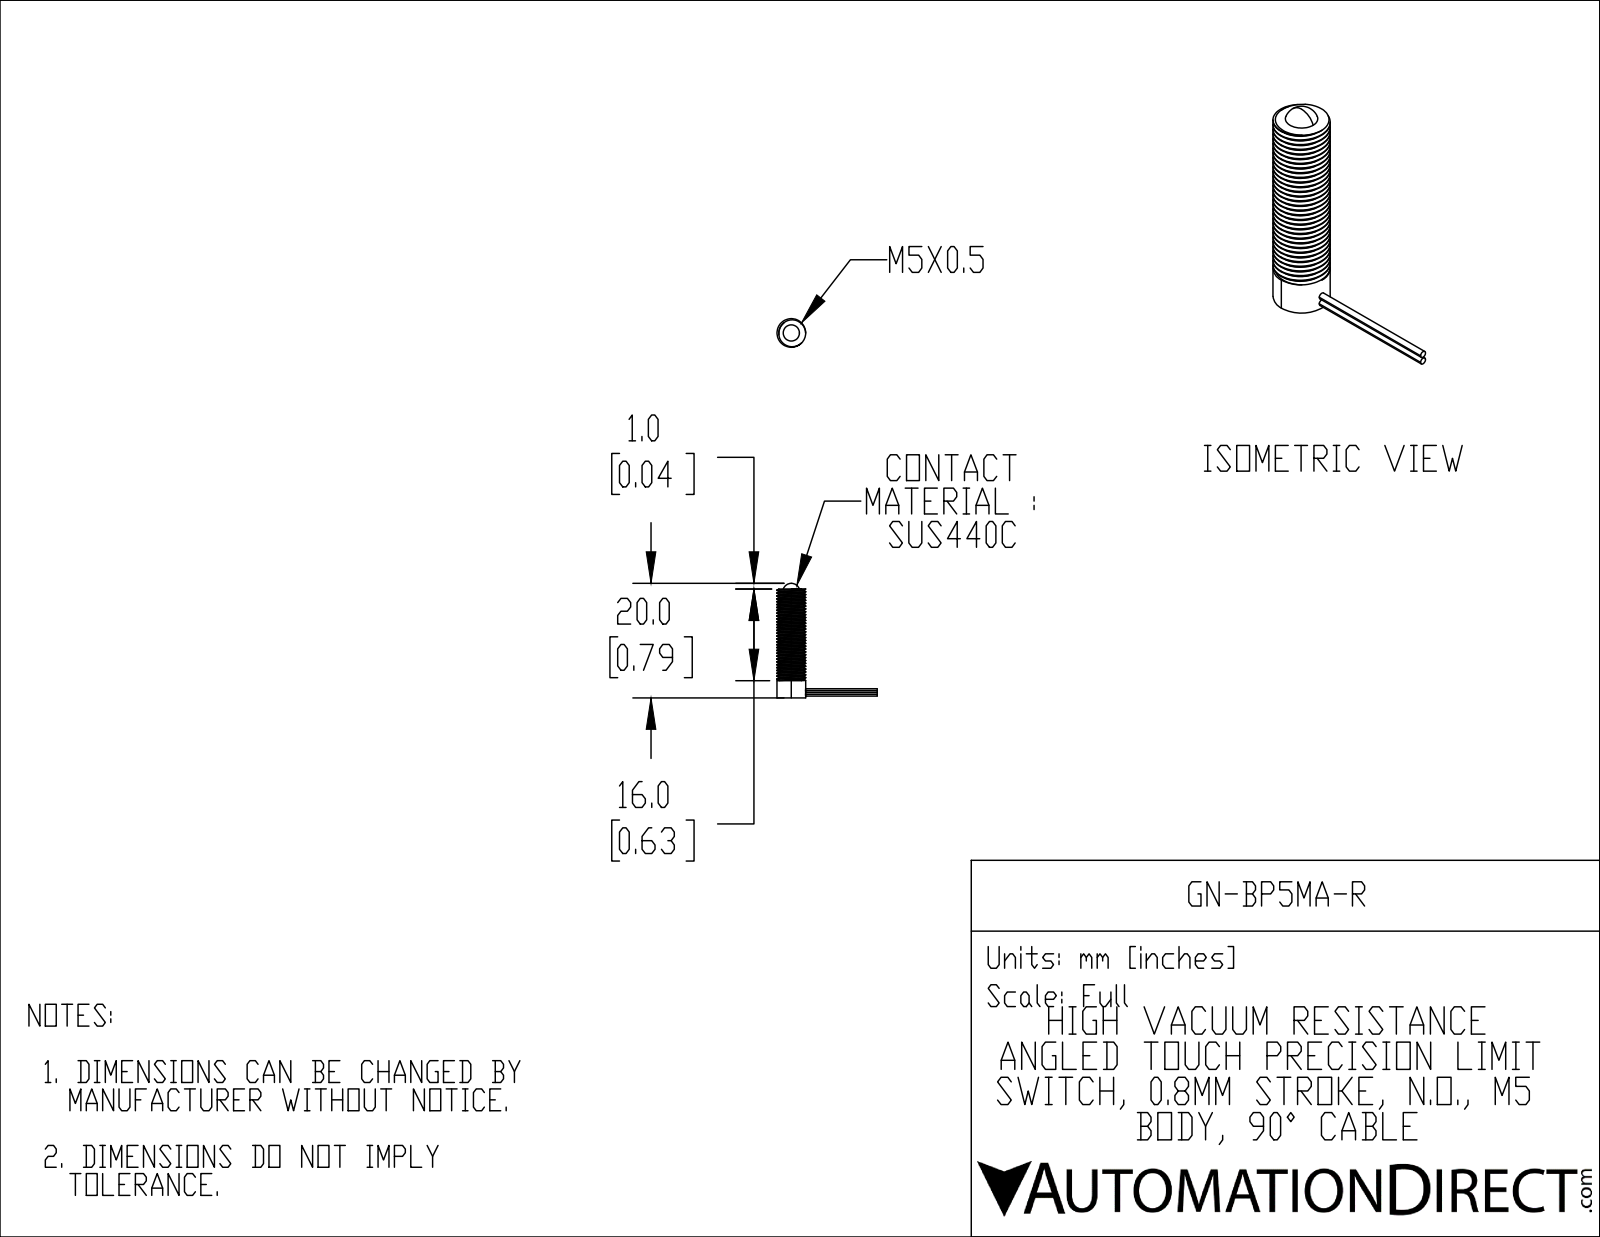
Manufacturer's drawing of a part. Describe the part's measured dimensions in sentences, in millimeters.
The part is named "GN-BP5MA-R". Its 3-D file was written by "SolidWorks 2020 (CONFIG_CONTROL_DESIGN)". It is 1 solid with 80 faces: 5 planar, 70 cylindrical and 5 other. Overall it measures 20 by 17.5 by 5 millimeters. Its volume is 344 cubic millimeters and its surface area 559 square millimeters. Round bosses or shafts: 2 of diameter 0.6, 1 of diameter 5. The main face-to-face distances are 19, 16, 3.
